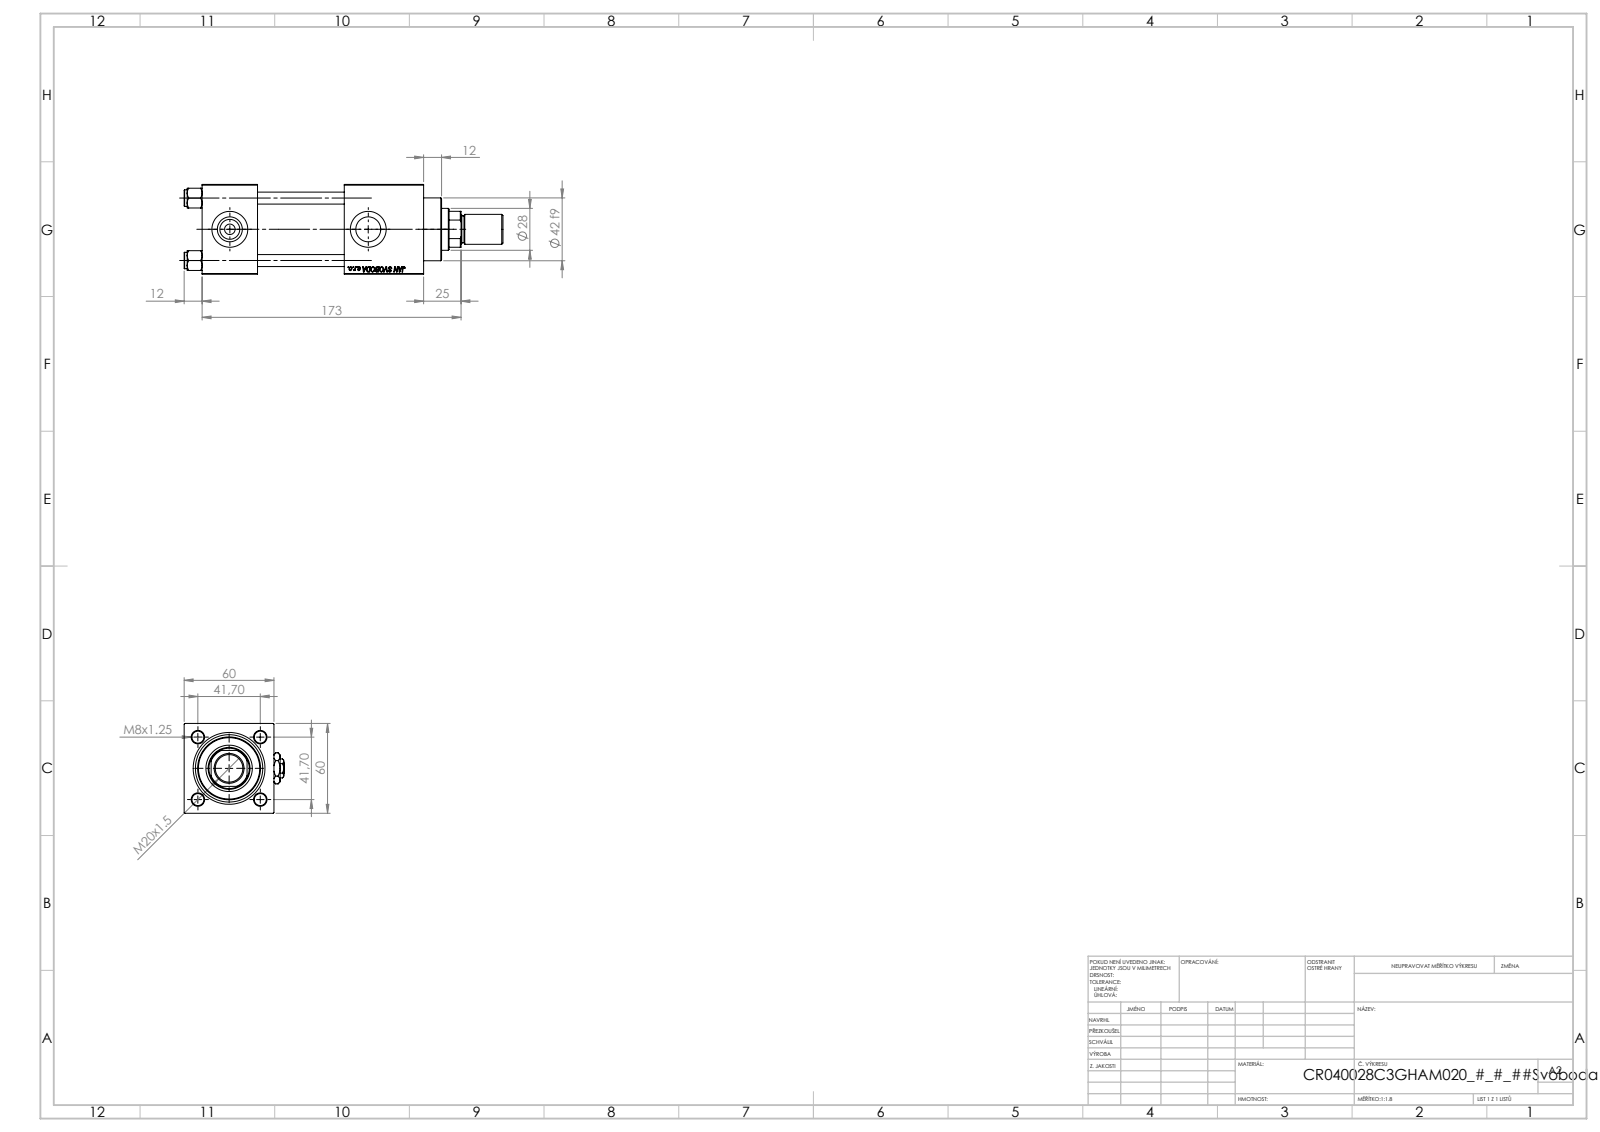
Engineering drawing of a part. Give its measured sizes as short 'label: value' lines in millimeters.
name: V215CR_C_TYCINKA; NUT_M5_C; ROD_END_AH; V215CR_C_Body (+3 more)
written by: SolidWorks 2019 (CONFIG_CONTROL_DESIGN)
unit: mm
bodies: 14 solids, 1264 faces (578 planar, 102 cylindrical, 584 other)
size: 213 × 67 × 60
volume: 429 590 mm³; area: 116 784 mm²
holes: 4× ⌀8, 2× ⌀7, 2× ⌀16.66, 2× ⌀24, 1× ⌀18.5, 1× ⌀28, 1× ⌀31, 1× ⌀40, 1× ⌀45
bosses: 4× ⌀11, 1× ⌀46, 1× ⌀42, 1× ⌀20, 1× ⌀18
rounds: 1× R13.5
face distances: 60, 37, 58, 53, 95, 119.3, 82.3, 24.3, 148, 111
hole spacings: 29.49, 41.7, 58.97, 92.5
